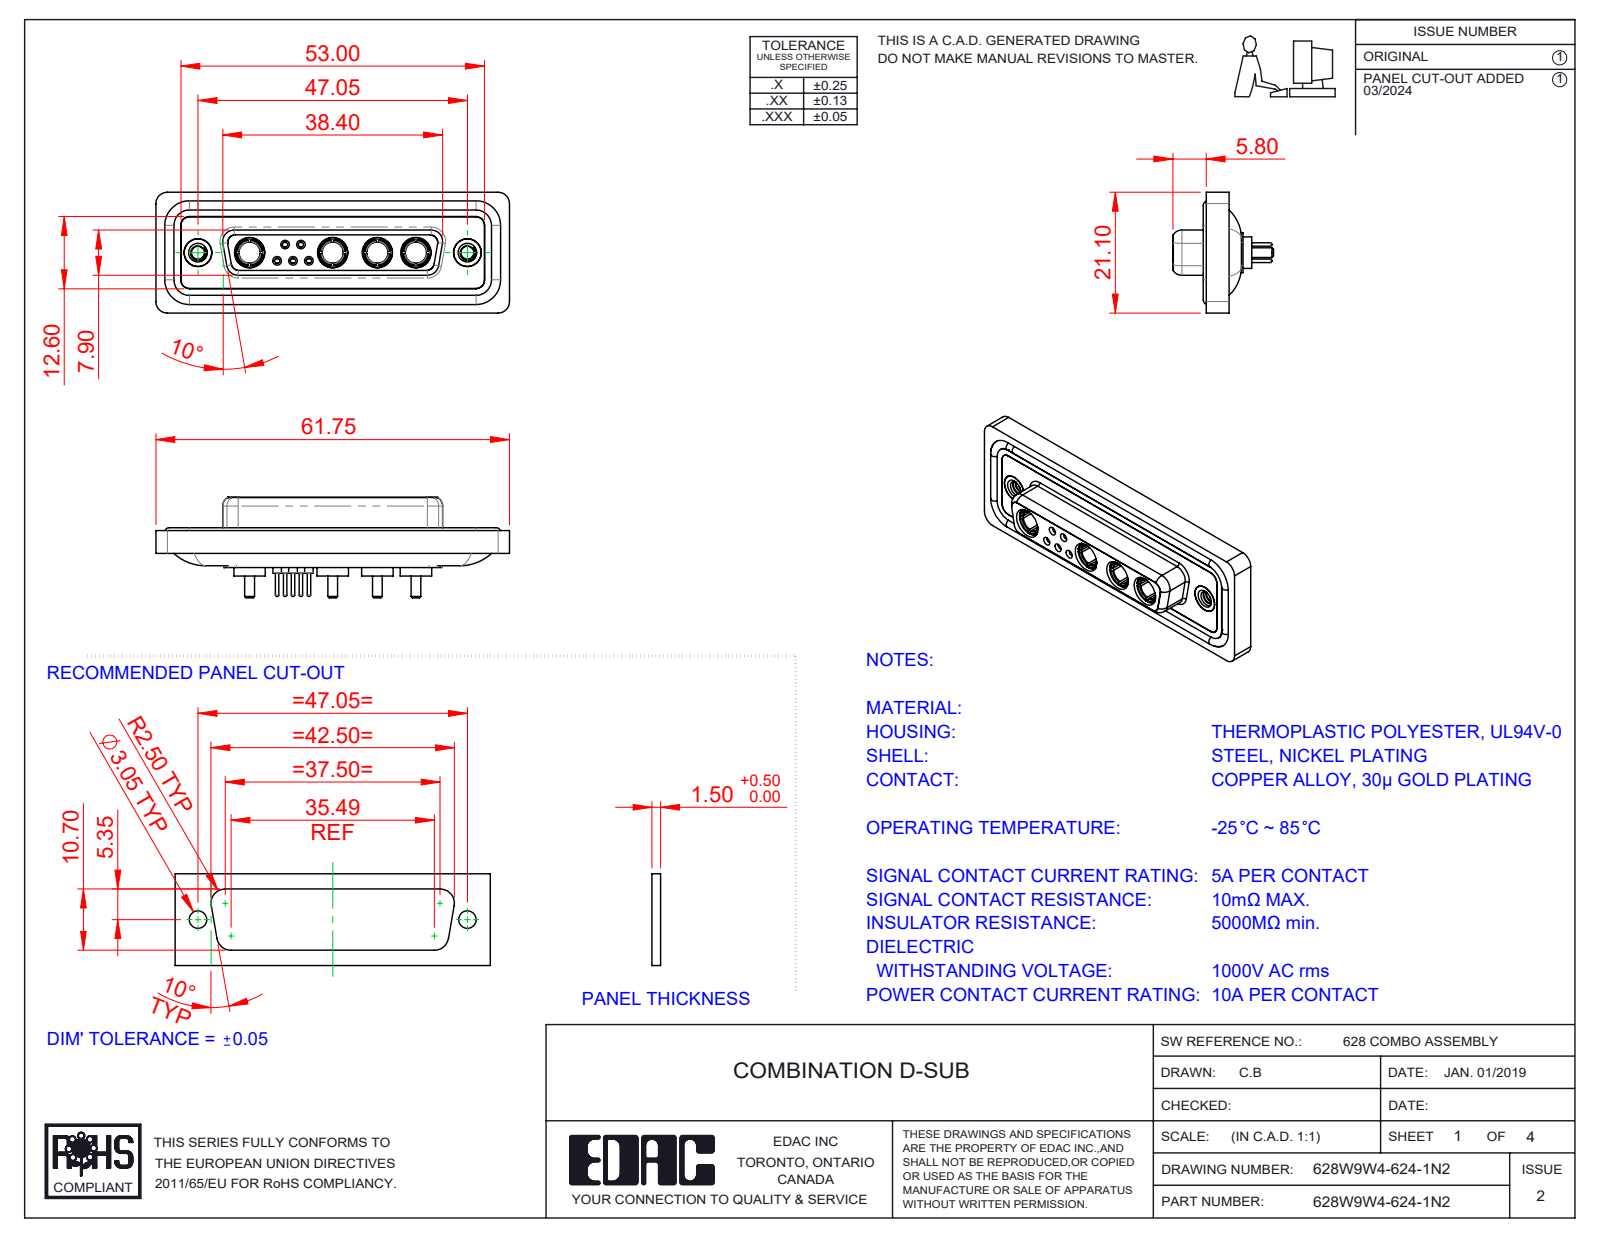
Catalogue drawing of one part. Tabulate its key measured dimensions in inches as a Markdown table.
| quantity | value |
| --- | --- |
| part name | 628Combo Shell Rear_25 Contacts; 628W9W4-624-1N2; 628Combo Contact Row 1_24; 628Combo Housing_9W4 (+5 more) |
| STEP written by | SolidWorks 2023 (CONFIG_CONTROL_DESIGN) |
| units | inches |
| bodies | 20 solids, 957 faces (296 planar, 375 cylindrical, 286 other) |
| overall size | 2.431 × 0.831 × 0.691 |
| volume | 0.498 in³ |
| surface area | 20.94 in² |
| round holes (diameter × count) | 0.191 × 6, 0.035 × 5, 0.043 × 5, 0.059 × 5, 0.079 × 5, 0.146 × 4, 0.209 × 4, 0.063 × 3, 0.067 × 2, 0.089 × 2, 0.157 × 2, 0.159 × 2 |
| round bosses / shafts (diameter × count) | 0.063 × 6, 0.087 × 5, 0.024 × 5, 0.217 × 4, 0.205 × 4, 0.195 × 4, 0.187 × 4, 0.148 × 4 |
| partial cylindrical surfaces (radius × count) | 0.059 × 22, 0.079 × 18, 0.053 × 8, 0.063 × 8, 0.01 × 4, 0.02 × 4, 0.024 × 4, 0.026 × 4 |
| main face-to-face distances | 0.016, 0.071, 0.293, 0.222, 0.02, 0.278, 0.26, 0.063, 0.043, 0.114 |
| hole center spacings | 0.124, 0.109, 0.198, 0.109, 0.173, 0.198, 0.218, 0.226 |
